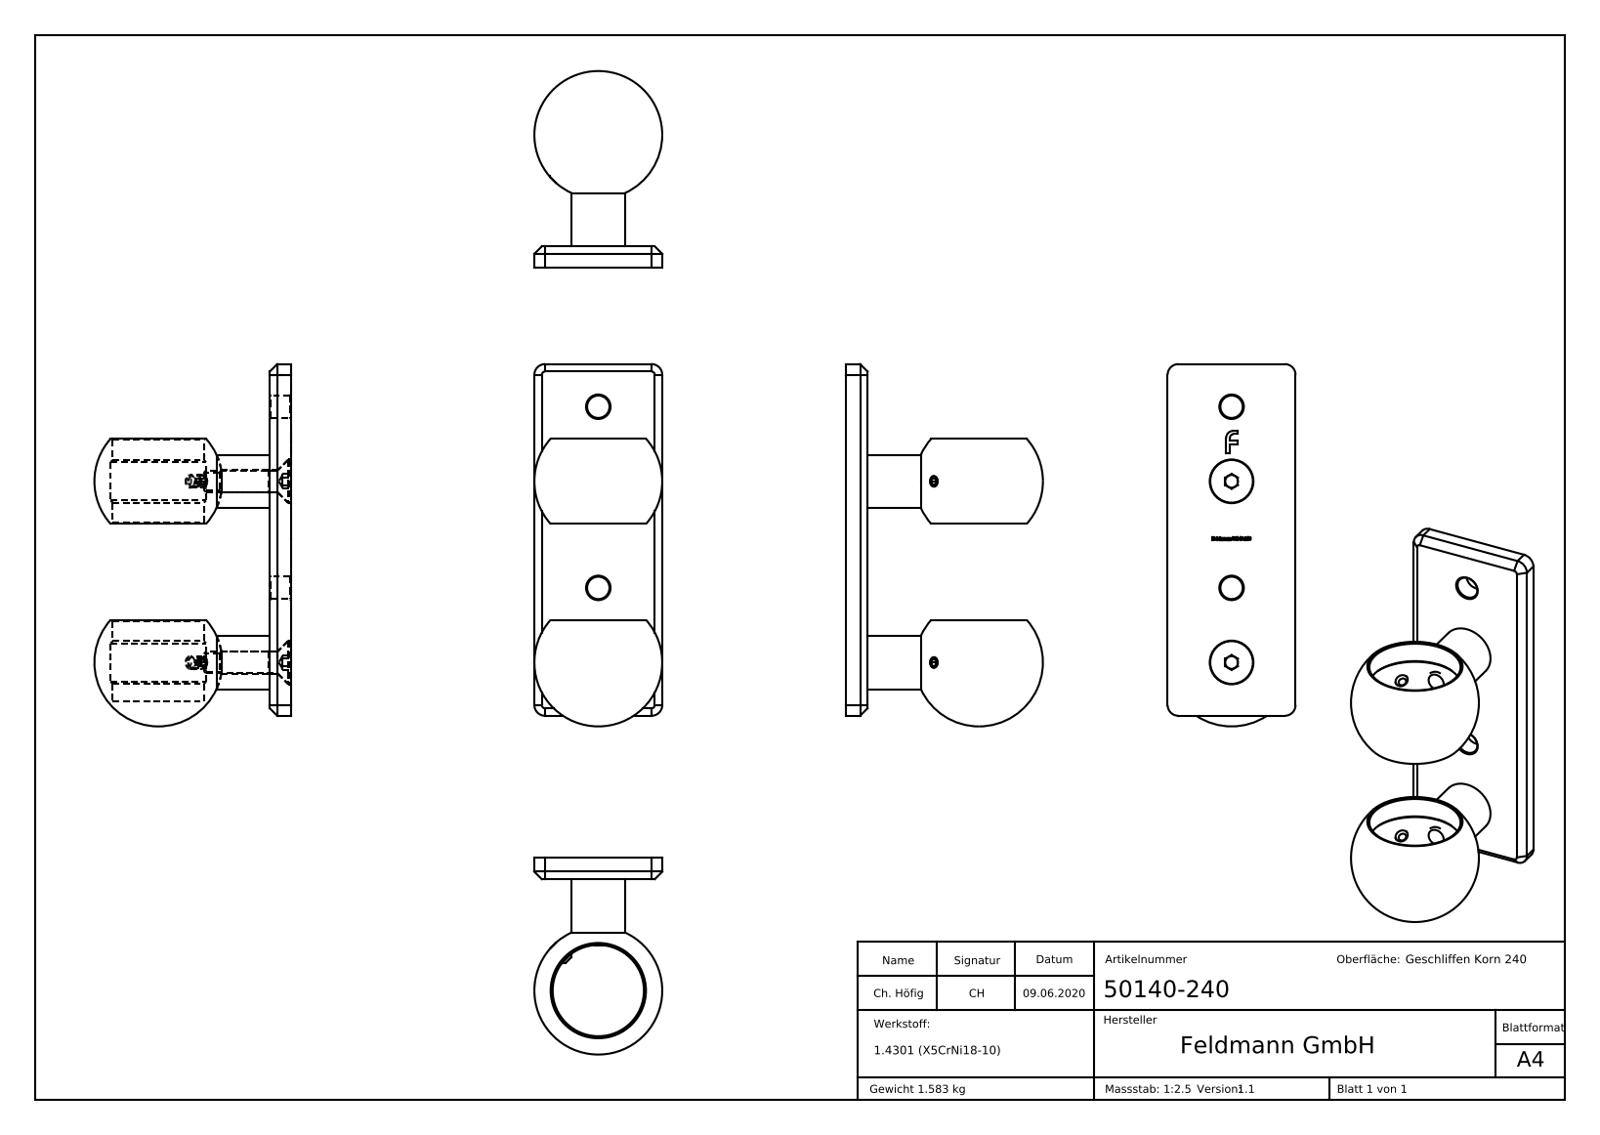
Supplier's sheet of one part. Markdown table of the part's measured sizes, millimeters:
| quantity | value |
| --- | --- |
| part name | DIN-7991 M3-M10; 5014X-240 Teil4_50140-240 Teil4; 50140-240; DIN913_DIN 913 M6x10 (+8 more) |
| STEP written by | SolidWorks 2015 (CONFIG_CONTROL_DESIGN) |
| units | millimeters |
| bodies | 9 solids, 368 faces (210 planar, 30 cylindrical, 128 other) |
| overall size | 53392.43 × 53046.36 × 10000.05 |
| volume | 200 428 mm³ |
| surface area | 65 106 mm² |
| round holes (diameter × count) | 10.5 × 4, 5 × 2, 8.5 × 2, 20.5 × 2, 42.8 × 1, 44.8 × 1 |
| round bosses / shafts (diameter × count) | 25 × 2, 20 × 2, 10 × 2, 6 × 2 |
| partial cylindrical surfaces (radius × count) | 5 × 4 |
| main face-to-face distances | 10, 60, 0.95, 9.05, 7, 165, 158, 40, 45, 40.95 |
| hole center spacings | 85, 35, 50, 120 |
